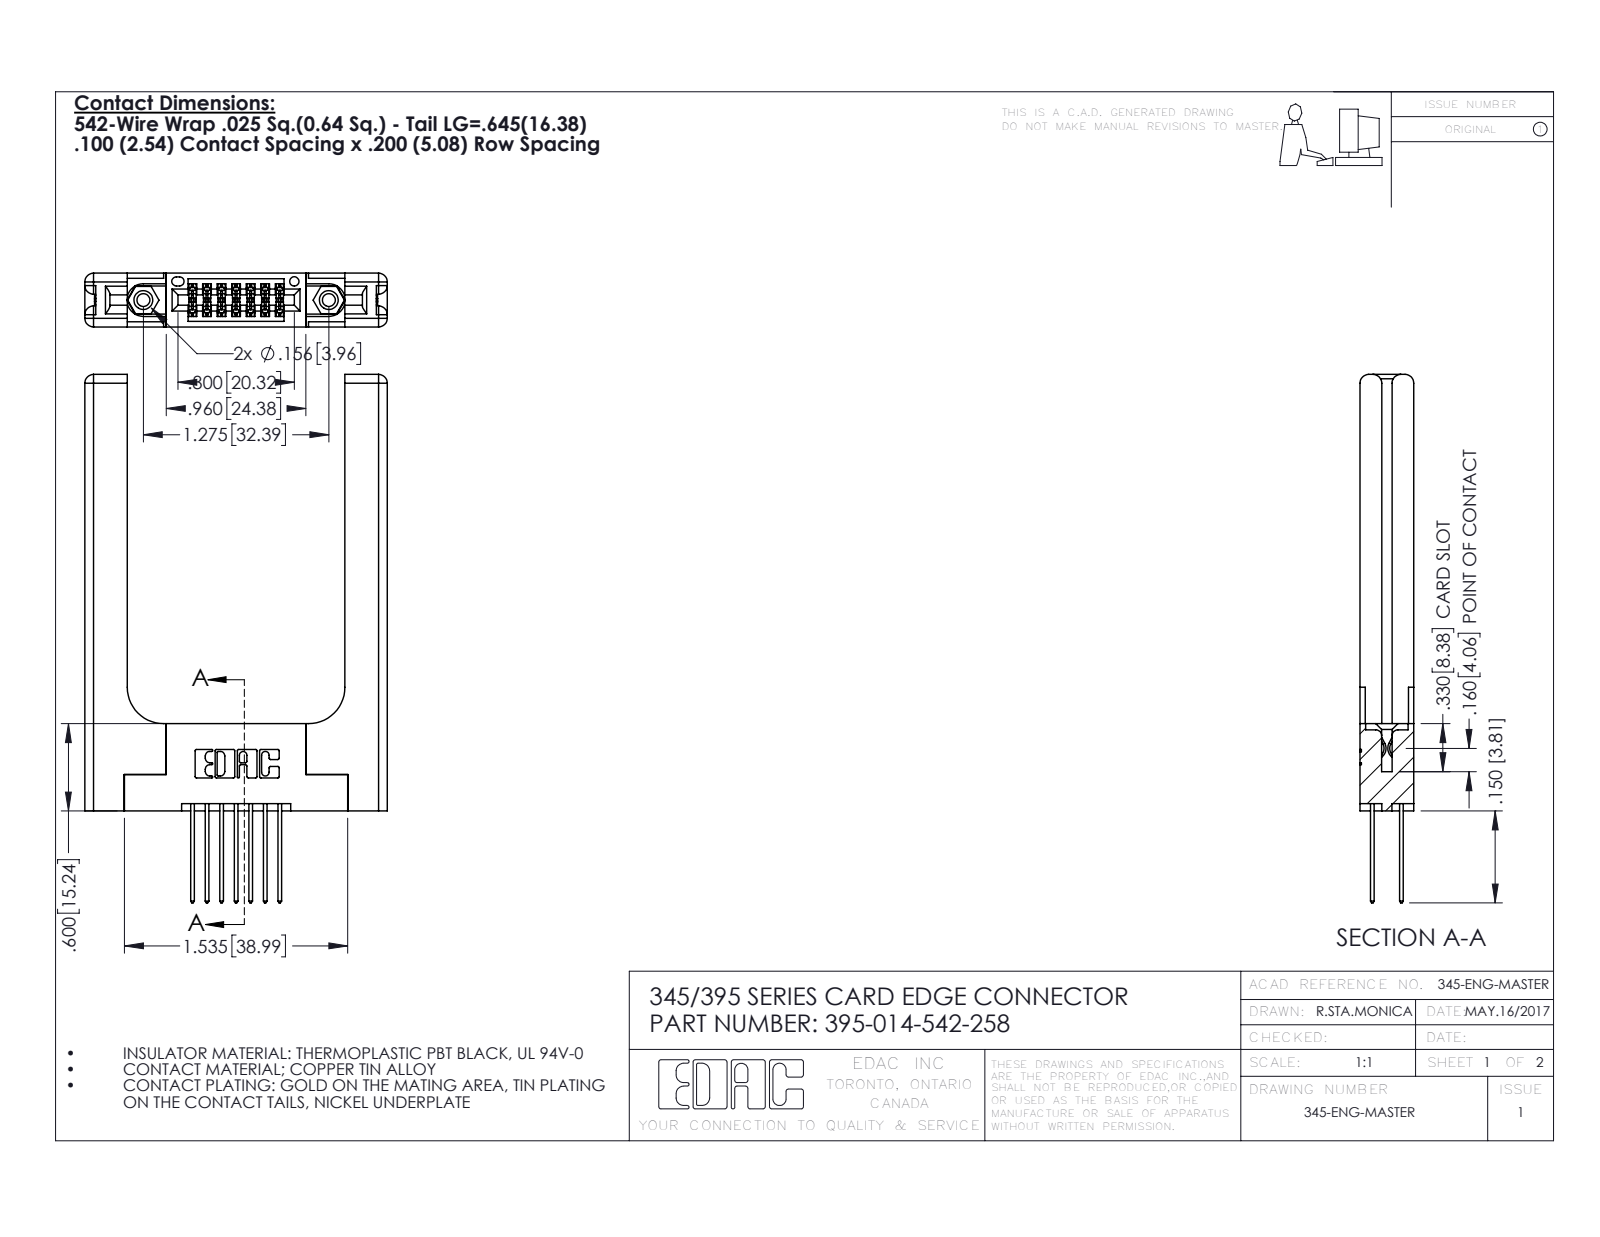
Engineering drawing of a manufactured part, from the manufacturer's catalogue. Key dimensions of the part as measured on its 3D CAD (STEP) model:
Part name (STEP PRODUCT): 345-292-001_345-293-142; 345-250-001_345-250-001-102; 345 Part_Flush Mounting Lugs - 0.156 Dia-TH; 395-014-542-258 (+1 more)
STEP written by: SolidWorks 2016 (CONFIG_CONTROL_DESIGN)
Units: inches
Bodies: 19 solids, 1082 faces (690 planar, 332 cylindrical, 60 other)
Overall size (bounding box): 3.632 × 2.079 × 0.37
Volume: 0.814 in³ · Surface area: 18.42 in²
Round holes (diameter × count): ⌀0.089 ×2, ⌀0.125 ×2, ⌀0.156 ×2, ⌀0.064 ×1
Round bosses / shafts (diameter × count): ⌀0.155 ×2
Partial cylindrical surfaces — rounded edges, fillets, slot ends (radius × count): R0.01 ×22, R0.006 ×21, R0.06 ×16, R0.01 ×14, R0.007 ×6, R0.031 ×6, R0.026 ×3, R0.014 ×2
Main face-to-face distances: 0.37, 0.072, 0.15, 0.22, 0.077, 0.148, 0.298, 0.2, 1.496, 0.225
Hole centre spacings: 0.27, 1.045, 1.275
